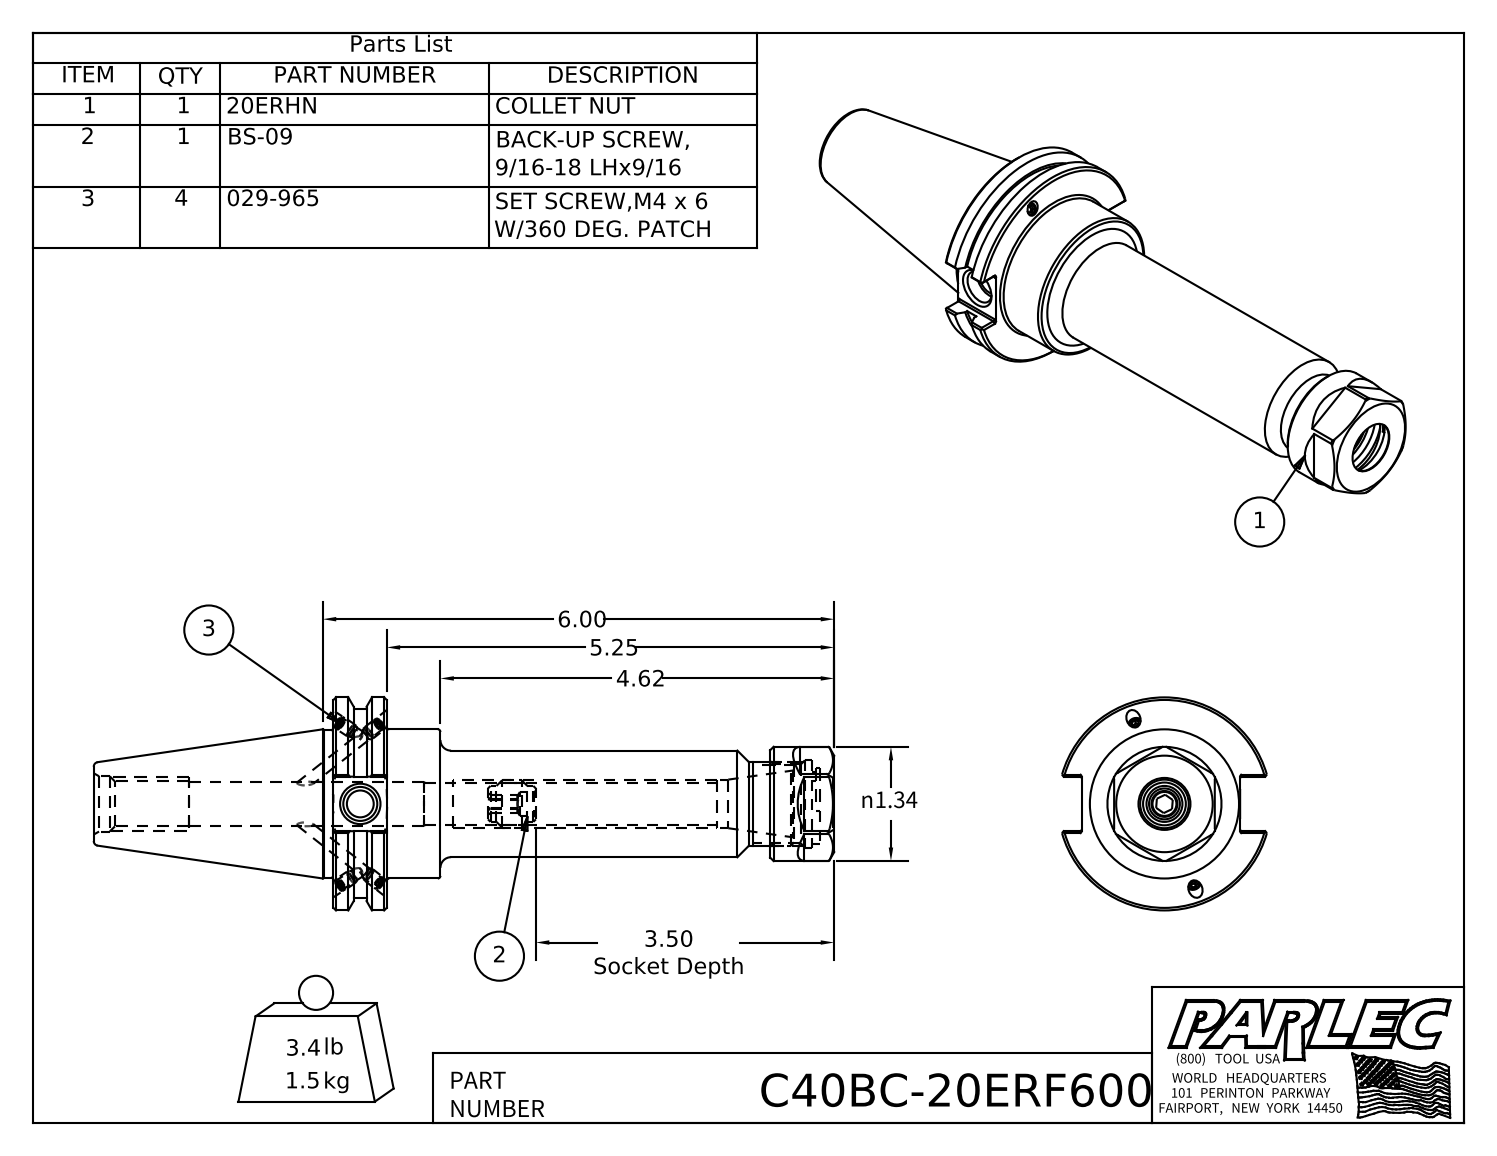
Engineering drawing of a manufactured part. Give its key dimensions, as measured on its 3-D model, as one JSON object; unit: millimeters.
{"part_name": "C40BCB-20ER6-1; 029-965; 20ERHN; BS-09 (+1 more)", "step_written_by": "Autodesk Inventor 2016 (AUTOMOTIVE_DESIGN)", "units": "millimeters", "bodies": {"solids": 7, "faces": 226, "planar": 108, "cylindrical": 60, "other": 58}, "overall_size": [220.66, 63.5, 61.05], "volume_mm3": 195558, "surface_area_mm2": 44040, "round_holes": [[3.3, 4], [4.1, 4], [7.14, 1], [8, 1], [10.13, 1], [12.75, 1], [13.36, 1], [13.39, 1], [14.48, 1], [15.49, 1], [16.46, 1], [23.5, 1]], "round_bosses_or_shafts": [[4.2, 4], [4, 4], [63.5, 1], [56.36, 1], [44.45, 1], [43.94, 1], [34, 1], [31.75, 1]], "partial_cylinders_radius": [[0.51, 12], [9.47, 1], [10.55, 1], [10.75, 1]], "face_to_face_distances": [15.87, 149.22, 133.35, 30, 31.87, 16, 117.35, 130.16, 114.29, 98.29]}
